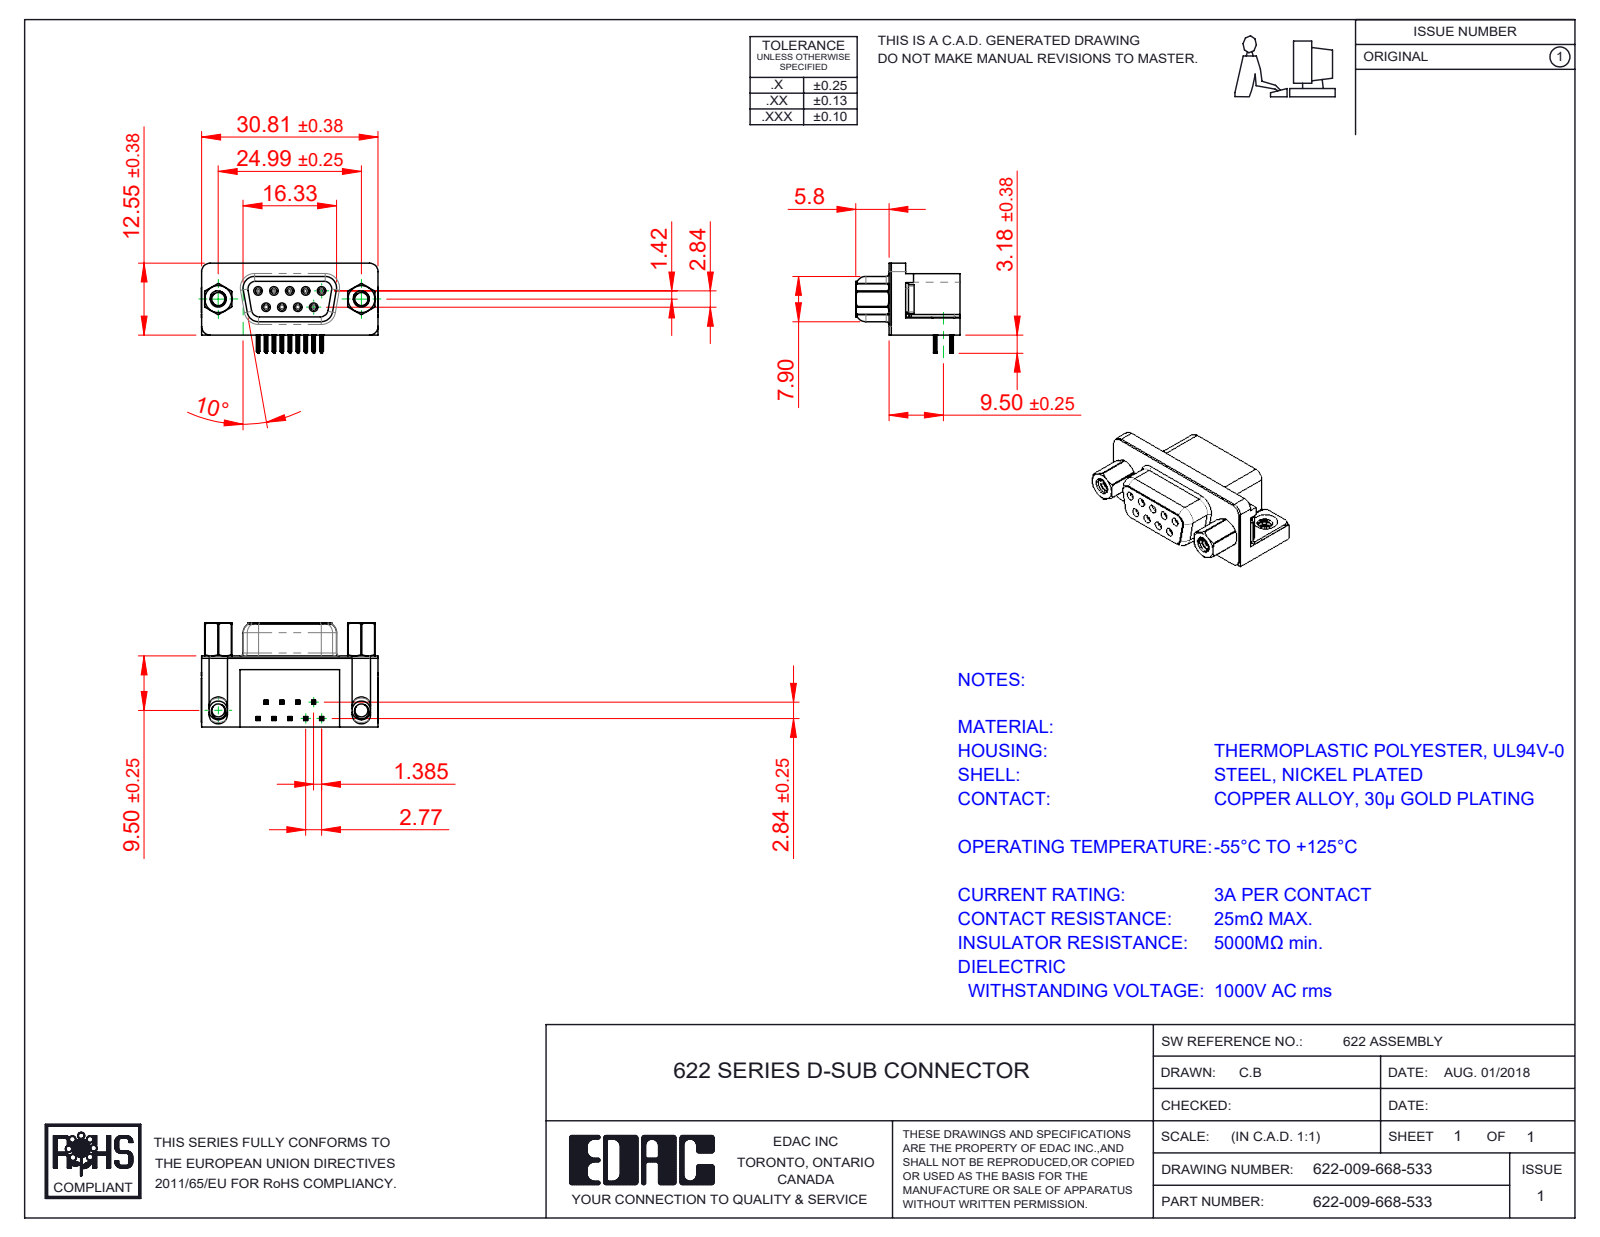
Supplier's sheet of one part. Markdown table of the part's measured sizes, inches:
| quantity | value |
| --- | --- |
| part name | 622 2 Prong Board Lock; 622-009-668-533; 622 Socket Bottom; 622 Contact Top (+4 more) |
| STEP written by | SolidWorks 2016 (CONFIG_CONTROL_DESIGN) |
| units | inches |
| bodies | 17 solids, 1732 faces (738 planar, 488 cylindrical, 506 other) |
| overall size | 1.216 × 0.717 × 0.64 |
| volume | 0.24 in³ |
| surface area | 8.575 in² |
| round holes (diameter × count) | 0.031 × 9, 0.035 × 9, 0.089 × 2, 0.09 × 2, 0.157 × 2, 0.189 × 2, 0.197 × 2 |
| round bosses / shafts (diameter × count) | 0.047 × 9, 0.193 × 2, 0.187 × 2, 0.154 × 2, 0.11 × 2 |
| partial cylindrical surfaces (radius × count) | 0.004 × 72, 0.006 × 36, 0.014 × 18, 0.039 × 18, 0.02 × 10, 0.013 × 9, 0.01 × 8, 0.053 × 8 |
| main face-to-face distances | 0.016, 0.472, 0.488, 0.244, 0.014, 0.114, 0.098, 0.407, 0.02, 0.228 |
| hole center spacings | 0.124, 0.109, 0.218, 0.198, 0.198, 0.327, 0.294, 0.295 |
